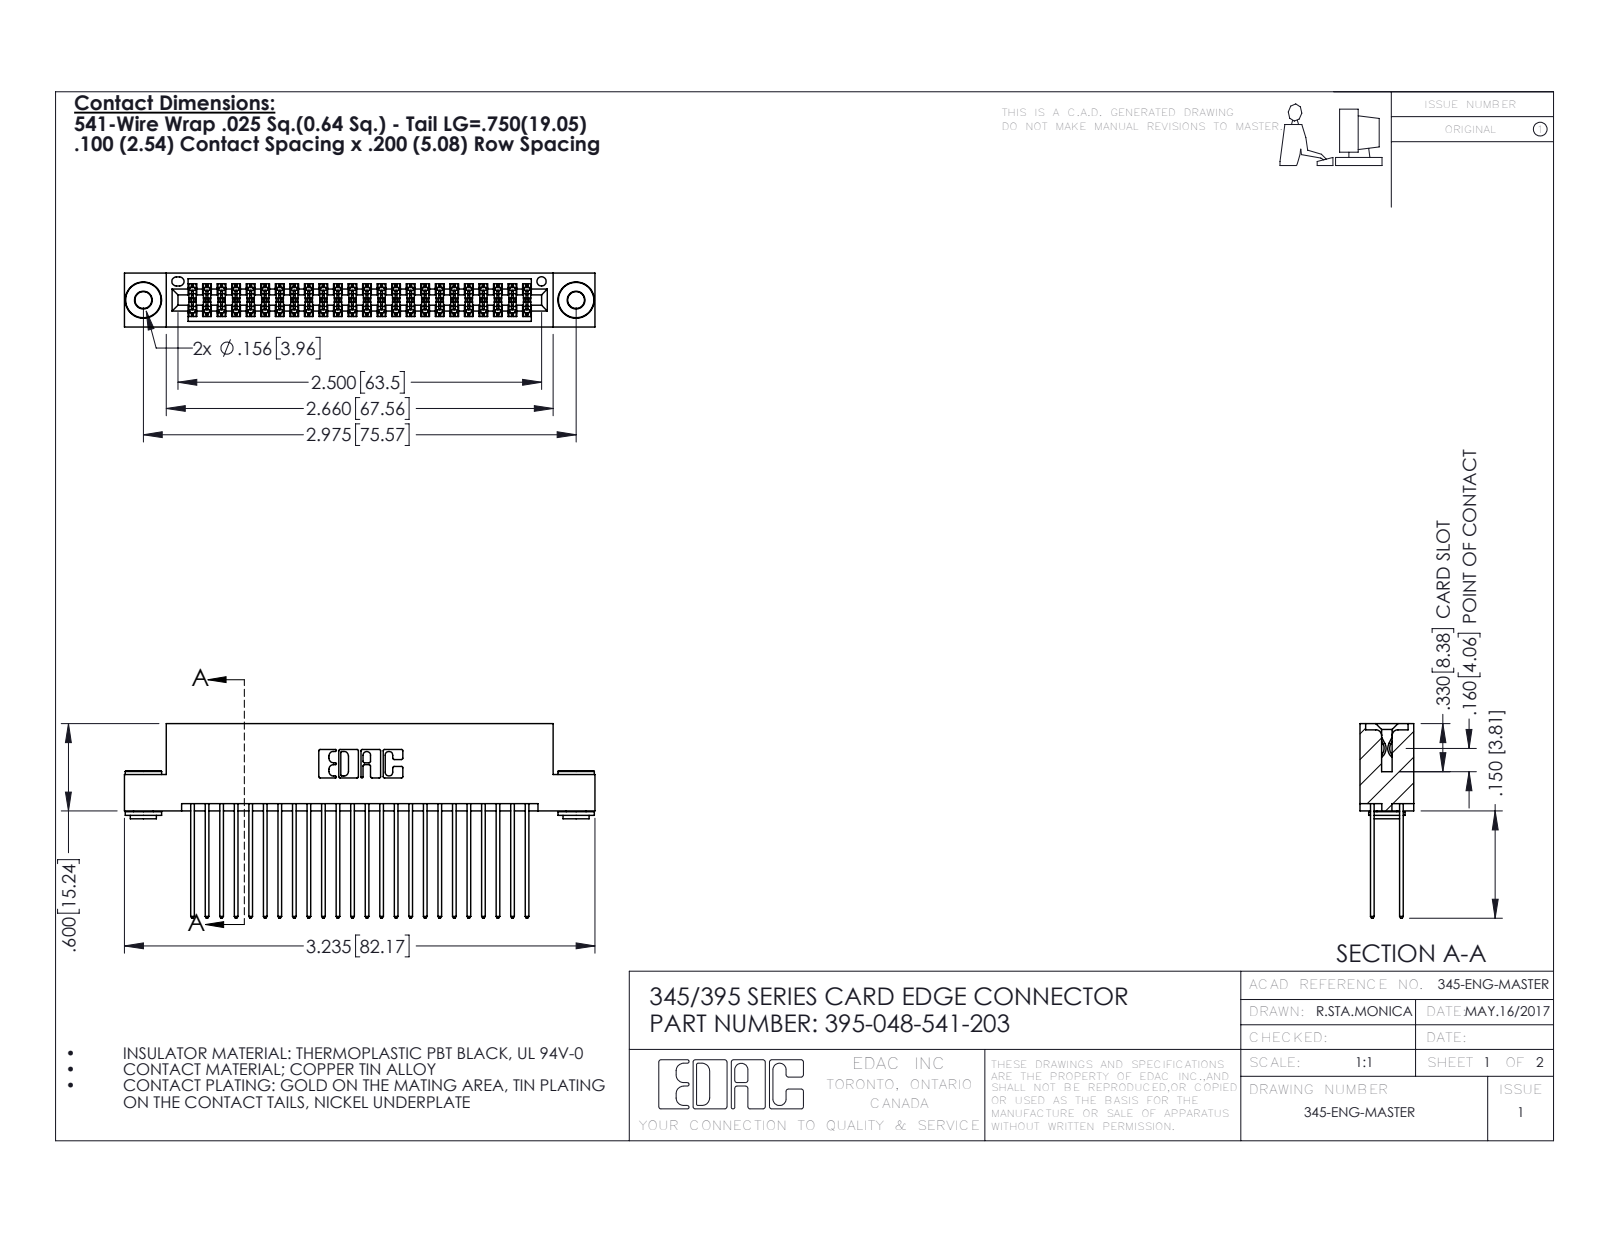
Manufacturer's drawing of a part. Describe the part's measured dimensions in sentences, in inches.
The part is named "345-250-002_345-250-002-102; 345-292-001_345-293-141; 395-048-541-203; 345 Part_Flush Mounting Lugs - 0.156 Dia-TH". Its 3-D file was written by "SolidWorks 2016 (CONFIG_CONTROL_DESIGN)". It is 51 solids with 2564 faces: 1674 planar, 882 cylindrical and 8 other. Overall it measures 3.235 by 1.337 by 0.37 inches. Its volume is 0.495 cubic inches and its surface area 20.36 square inches. Round holes: 2 of diameter 0.116, 2 of diameter 0.156, 1 of diameter 0.064. Round bosses or shafts: 2 of diameter 0.25, 2 of diameter 0.18, 2 of diameter 0.136. Partial cylindrical surfaces (rounded edges, fillets, slot ends): 72 of radius 0.006, 48 of radius 0.01, 22 of radius 0.01, 6 of radius 0.007, 6 of radius 0.031, 3 of radius 0.026, 2 of radius 0.014, 2 of radius 0.019. The main face-to-face distances are 0.072, 0.298, 0.2, 0.025, 0.098, 0.272, 0.225, 0.37, 0.175, 0.149. The hole center spacings are 0.27, 2.741, 2.975.
